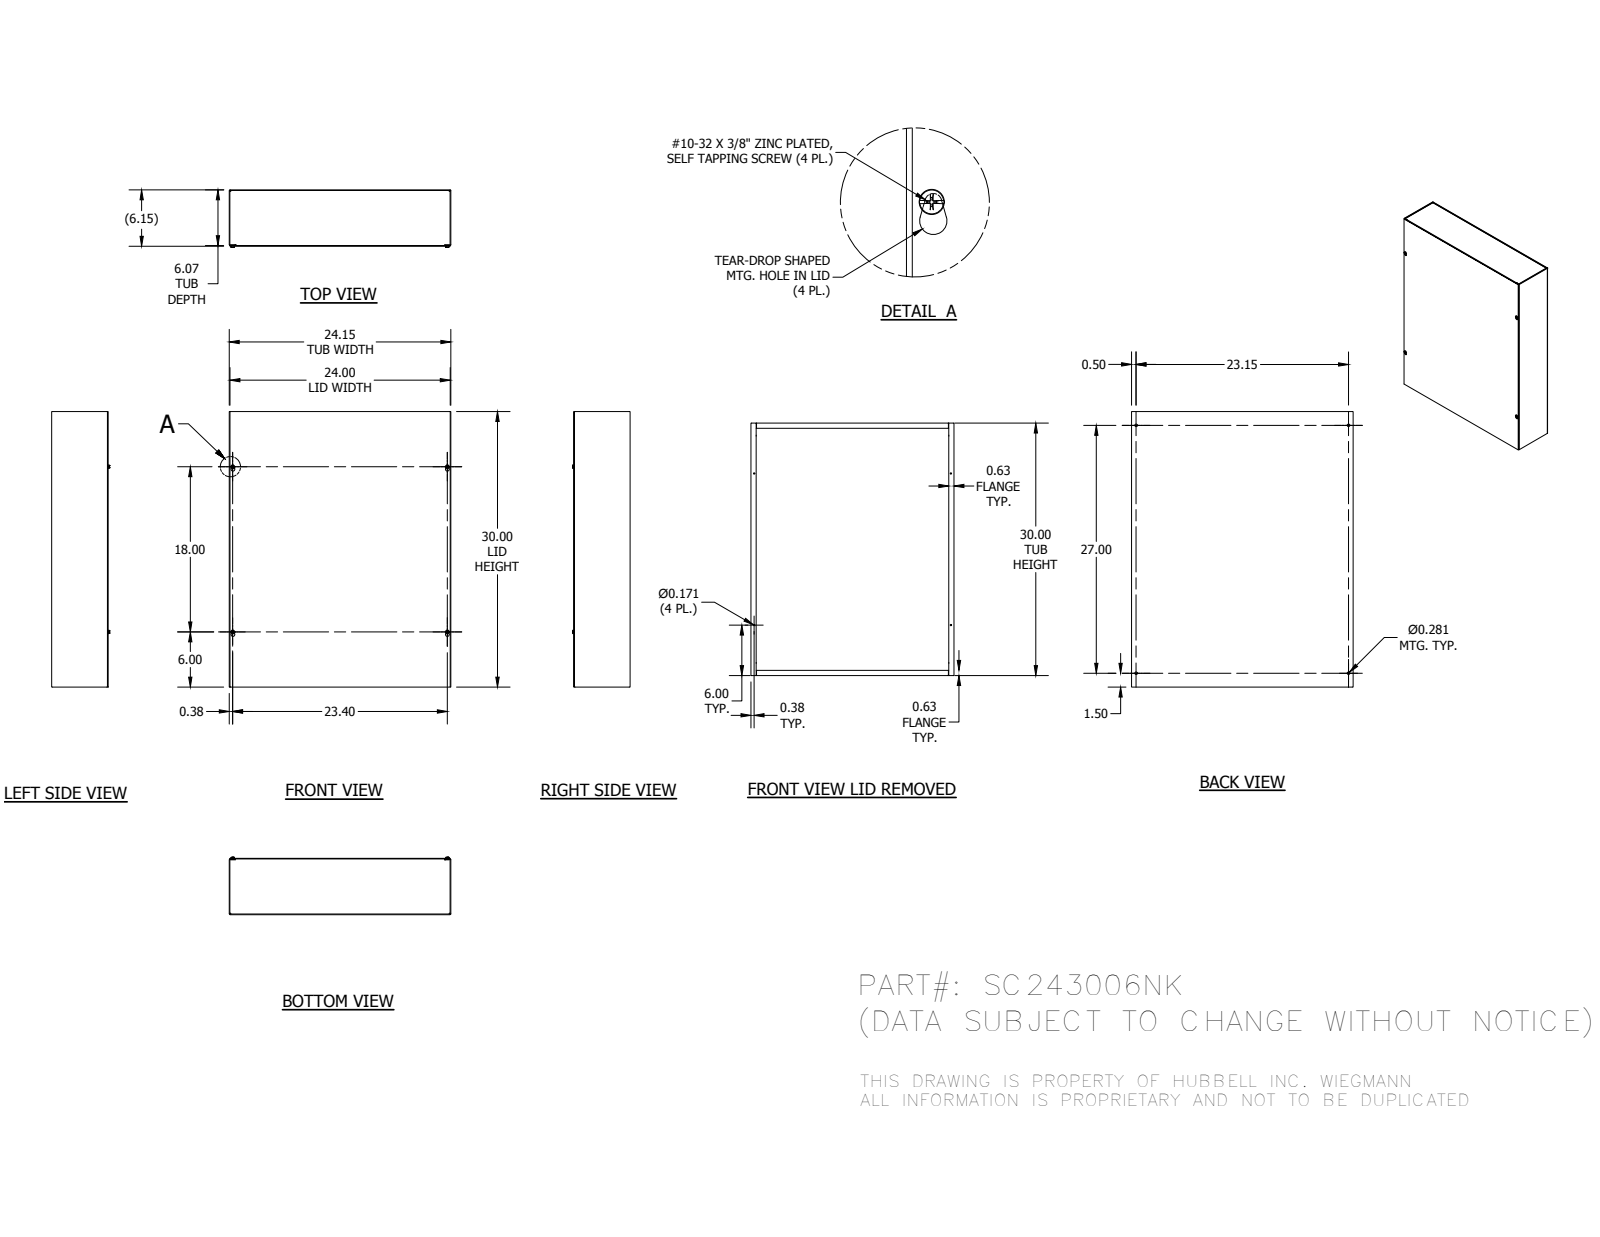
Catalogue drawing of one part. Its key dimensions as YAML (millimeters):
part_name: "SC243006NKBLR; SC2406NKTB; SC2430LPA; 37214 (+1 more)"
step_written_by: "Autodesk Inventor 2014 (AUTOMOTIVE_DESIGN)"
units: millimeters
bodies: {solids: 8, faces: 320, planar: 192, cylindrical: 44, other: 84}
overall_size: [762, 613.36, 159.51]
volume: 2649000
surface_area: 2837000
round_holes:
  - {diameter: 4.34, count: 4}
  - {diameter: 7.14, count: 4}
round_bosses_or_shafts:
  - {diameter: 4.83, count: 4}
partial_cylinders:
  - {radius: 0.4, count: 12}
  - {radius: 2.28, count: 12}
  - {radius: 3.17, count: 4}
  - {radius: 5.16, count: 4}
face_to_face_distances: [1.88, 154.28, 152.4, 156.16, 611.48, 760.12, 609.6, 613.36, 762, 758.24]
hole_center_spacings: [114.34, 571.51, 602.08, 822.22, 457.2, 587.96, 594.3, 685.8]
